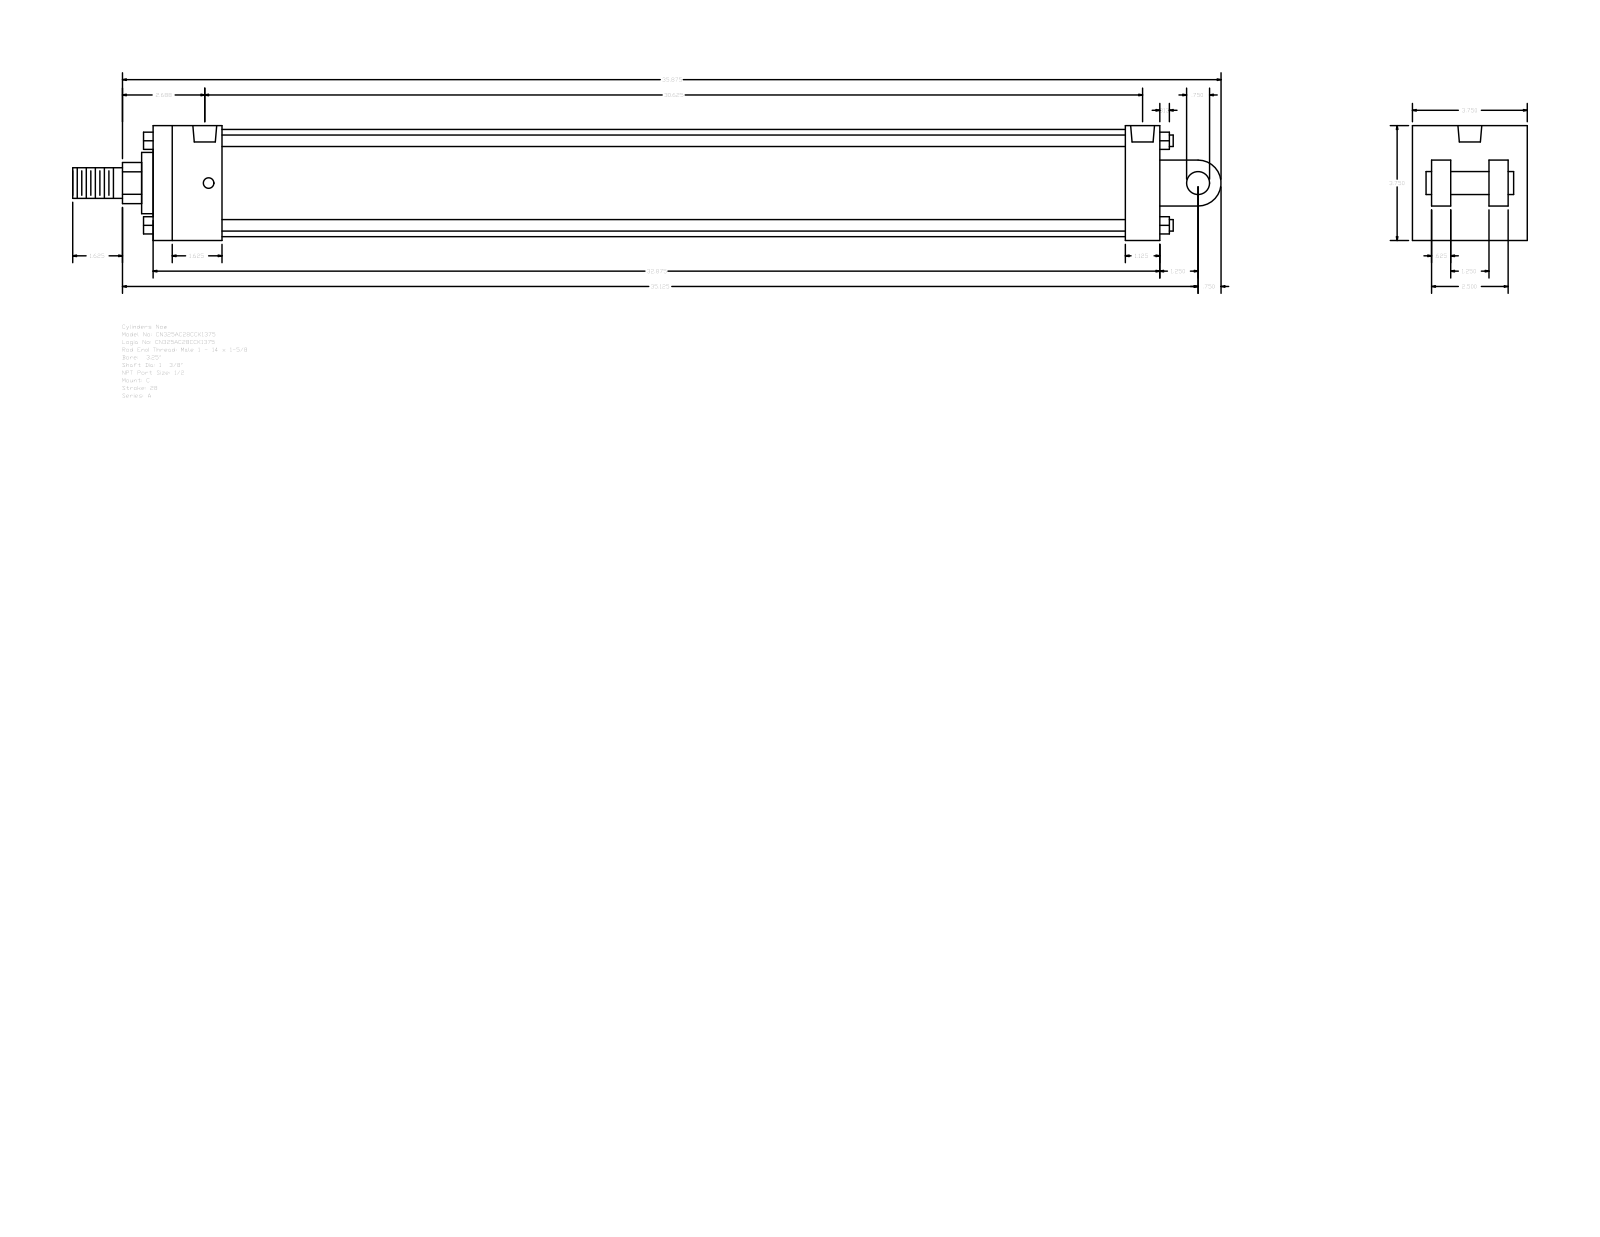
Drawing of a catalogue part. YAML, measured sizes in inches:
part_name: "A_C__0325_1.375"
step_written_by: "GSSL Pune (CONFIG_CONTROL_DESIGN)"
units: inches
bodies: {solids: 0, faces: 135, planar: 102, cylindrical: 33, other: 0}
overall_size: [37.5, 3.75, 3.75]
round_holes:
  - {diameter: 0.344, count: 4}
  - {diameter: 0.778, count: 2}
round_bosses_or_shafts:
  - {diameter: 0.375, count: 4}
  - {diameter: 3.5, count: 1}
  - {diameter: 2, count: 1}
  - {diameter: 1.375, count: 1}
  - {diameter: 1, count: 1}
  - {diameter: 0.75, count: 1}
partial_cylinders:
  - {radius: 0.672, count: 1}
  - {radius: 0.75, count: 1}
face_to_face_distances: [3.75, 32.875, 0.625, 1.125, 2.5, 2.625, 2.25, 1.25, 3.125, 1.875]
hole_center_spacings: [0.125, 30.375, 30.5, 30.625]
